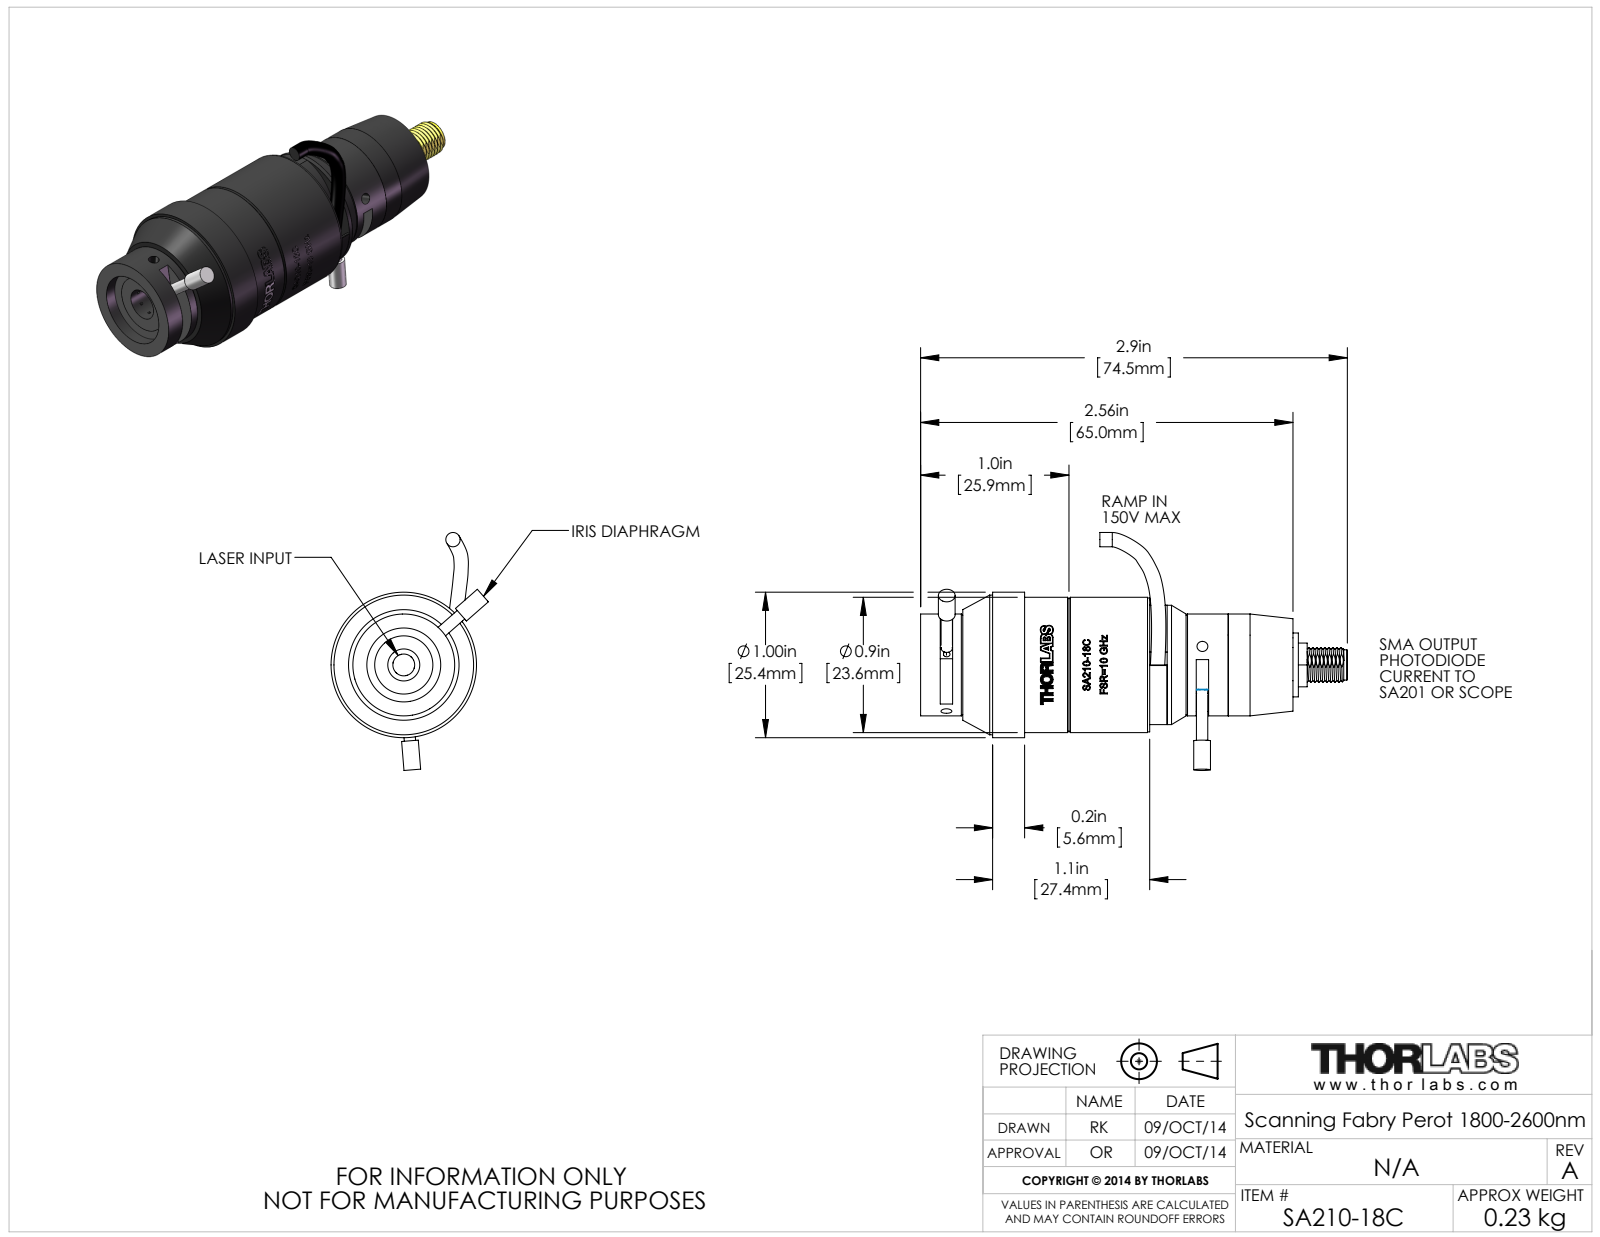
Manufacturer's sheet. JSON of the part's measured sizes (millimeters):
{"part_name": "STN012214-E0W1", "step_written_by": "SolidWorks 2014 (AUTOMOTIVE_DESIGN)", "units": "millimeters", "bodies": {"solids": 0, "faces": 290, "planar": 163, "cylindrical": 91, "other": 36}, "overall_size": [74.52, 41.54, 27.47], "round_holes": [[1.48, 10], [1.91, 6], [1, 1], [3.81, 1], [4.6, 1], [5.59, 1], [6.35, 1], [8.26, 1], [10.03, 1], [11.68, 1], [11.94, 1], [12.9, 1]], "round_bosses_or_shafts": [[2.92, 2], [1.98, 2], [25.4, 1], [24.38, 1], [23.62, 1], [23.37, 1], [23, 1], [21.84, 1]], "partial_cylinders_radius": [[0.1, 2], [0.36, 1], [1.05, 1], [1.55, 1], [1.55, 1], [1.91, 1], [7.16, 1], [8.71, 1]], "face_to_face_distances": [3.81, 2.54, 3.3, 31.04, 32.64, 7.37, 0.76, 2.03, 35.69, 43.81], "hole_center_spacings": [3.77, 6.53, 6.74, 0.43, 3.39, 4.14, 6.31, 6.54]}
